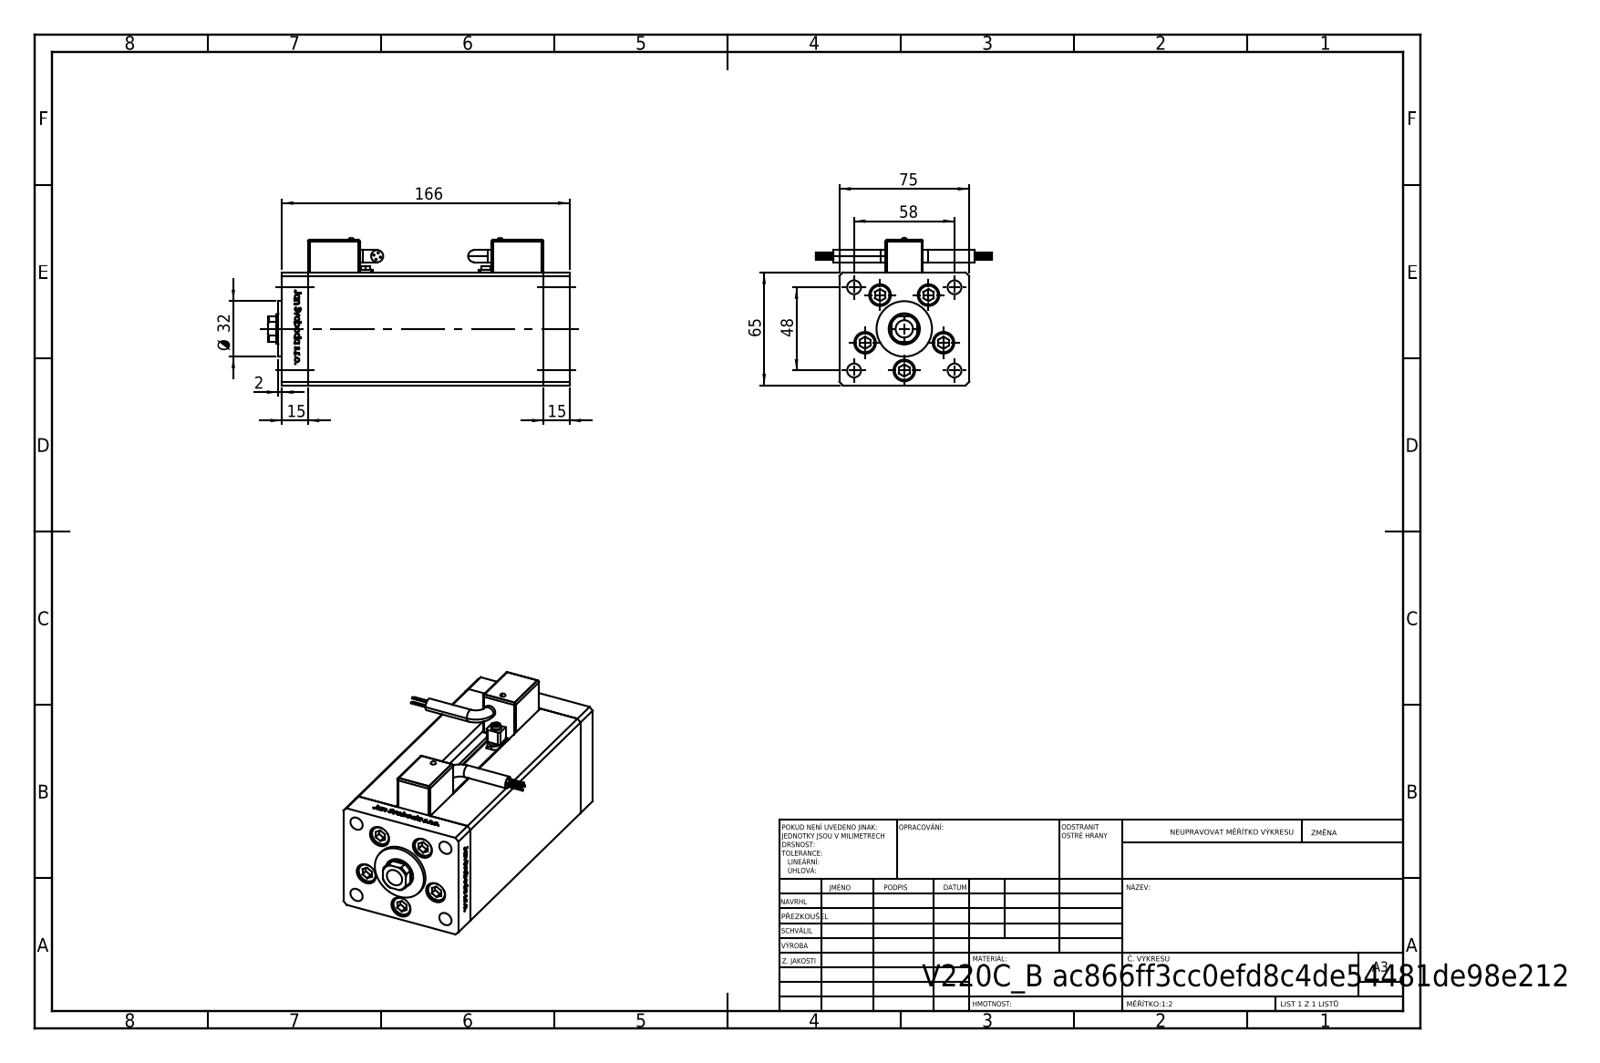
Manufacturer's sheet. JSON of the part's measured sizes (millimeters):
{"part_name": "V220C_B_VC; V220C BACK_B; V220C_B MIDDLE; V220C_FRONT_B (+2 more)", "step_written_by": "SolidWorks 2019 (CONFIG_CONTROL_DESIGN)", "units": "millimeters", "bodies": {"solids": 16, "faces": 1379, "planar": 538, "cylindrical": 233, "other": 608}, "overall_size": [174, 101.6, 85.1], "volume_mm3": 759332, "surface_area_mm2": 136919, "round_holes": [[9, 5], [12.5, 5], [8, 4], [2, 2], [3.6, 2], [5, 2], [7, 2], [13.16, 2], [10, 1], [18, 1]], "round_bosses_or_shafts": [[0.85, 8], [8, 5], [7, 4], [6, 2], [3.5, 2], [2.5, 2], [32, 1]], "partial_cylinders_radius": [[1, 24], [4, 4], [0.93, 2], [8.5, 1]], "face_to_face_distances": [75, 65, 136, 15, 151, 166, 48.3, 26.7, 58.5, 6.5], "hole_center_spacings": [24, 37.64, 8.25, 15.67, 17.22, 21.26, 27.71, 28]}
